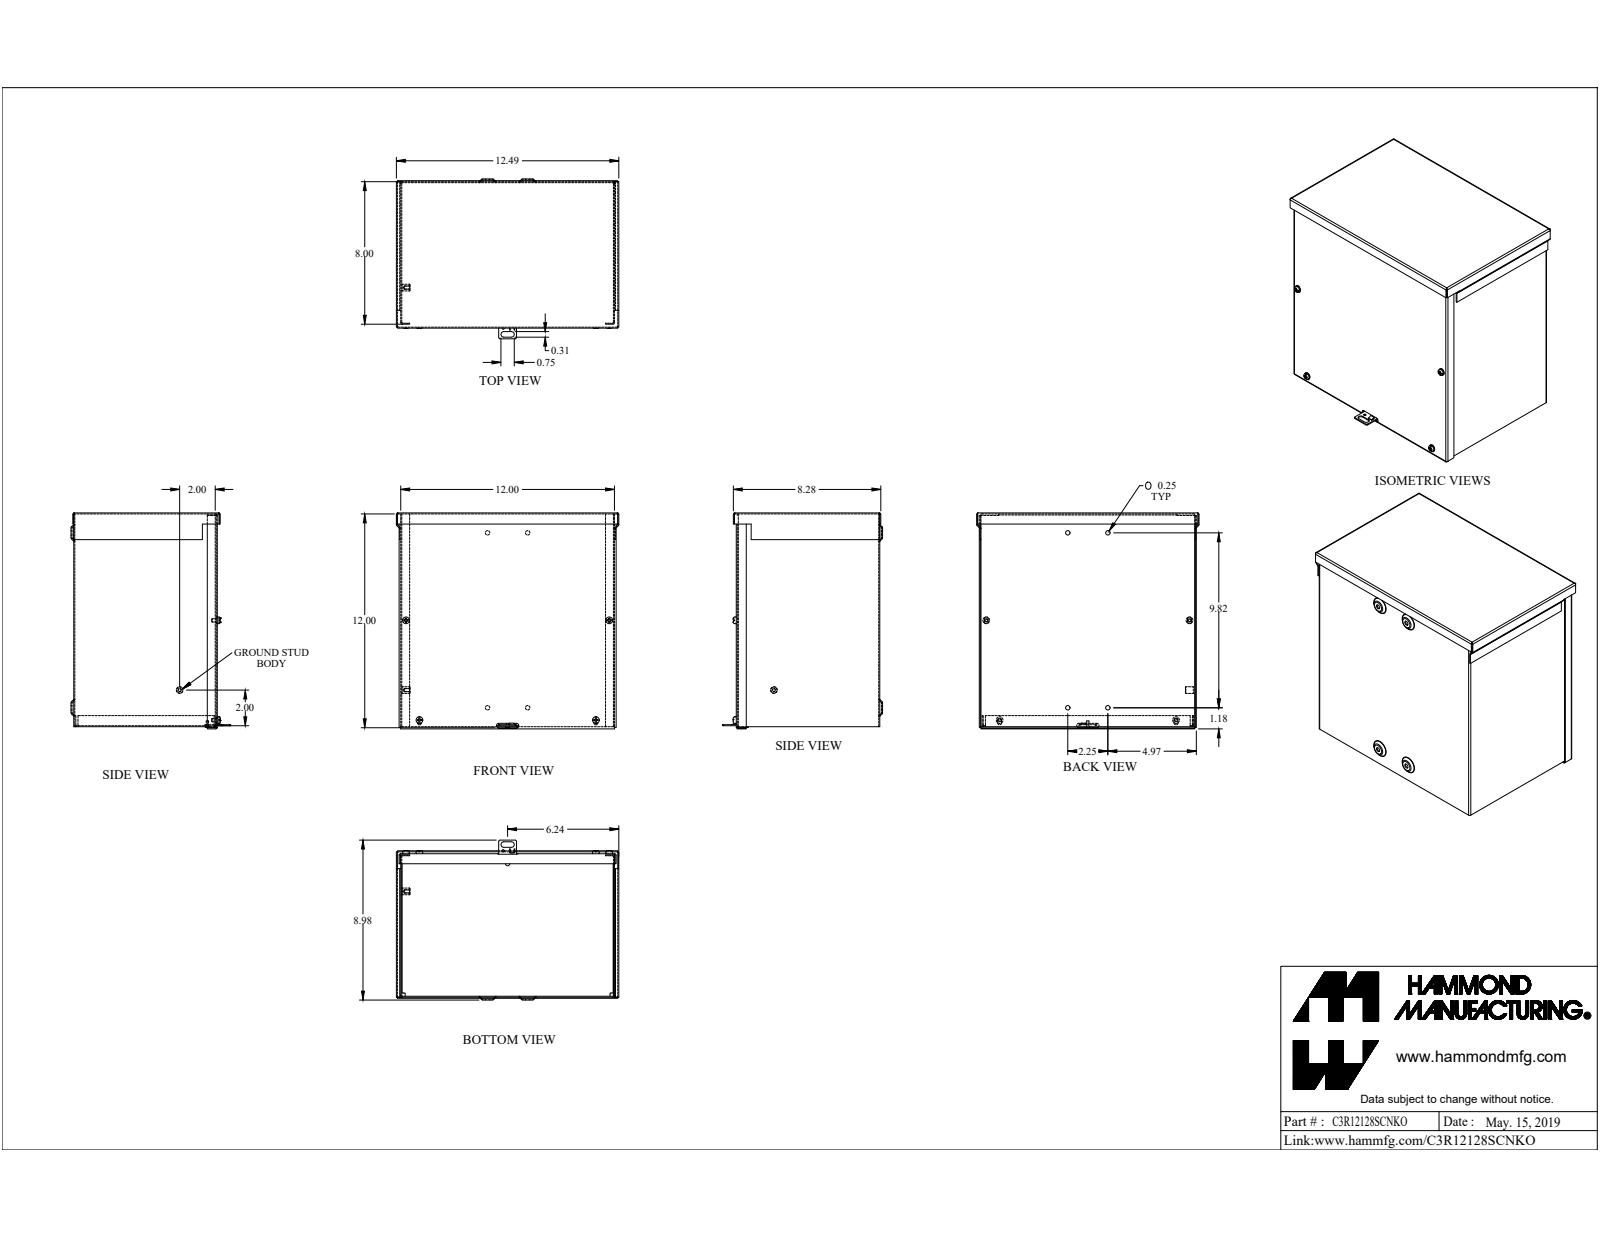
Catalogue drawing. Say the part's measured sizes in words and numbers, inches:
The part is named "C3R12128SCNKO". Its 3-D file was written by "SolidWorks 2019 (AUTOMOTIVE_DESIGN)". It is 11 solids with 339 faces: 211 planar, 84 cylindrical and 44 other. Overall it measures 12.489 by 12.086 by 8.977 inches. Its volume is 44.55 cubic inches and its surface area 1 545 square inches. Round holes: 4 of diameter 0.17, 4 of diameter 0.25, 1 of diameter 0.125, 1 of diameter 0.137, 1 of diameter 0.156. Round bosses or shafts: 4 of diameter 0.19, 3 of diameter 0.375, 2 of diameter 0.375, 1 of diameter 0.125. Partial cylindrical surfaces (rounded edges, fillets, slot ends): 21 of radius 0.029, 21 of radius 0.086, 8 of radius 0.109, 8 of radius 0.125, 2 of radius 0.156. The main face-to-face distances are 0.057, 8, 11.943, 12, 7.943, 8.057, 0.057, 11.943, 11.886, 11.886. The hole center spacings are 6.715, 8.413, 2.25, 3.92, 5.726, 6.142, 9.818, 10.072.
